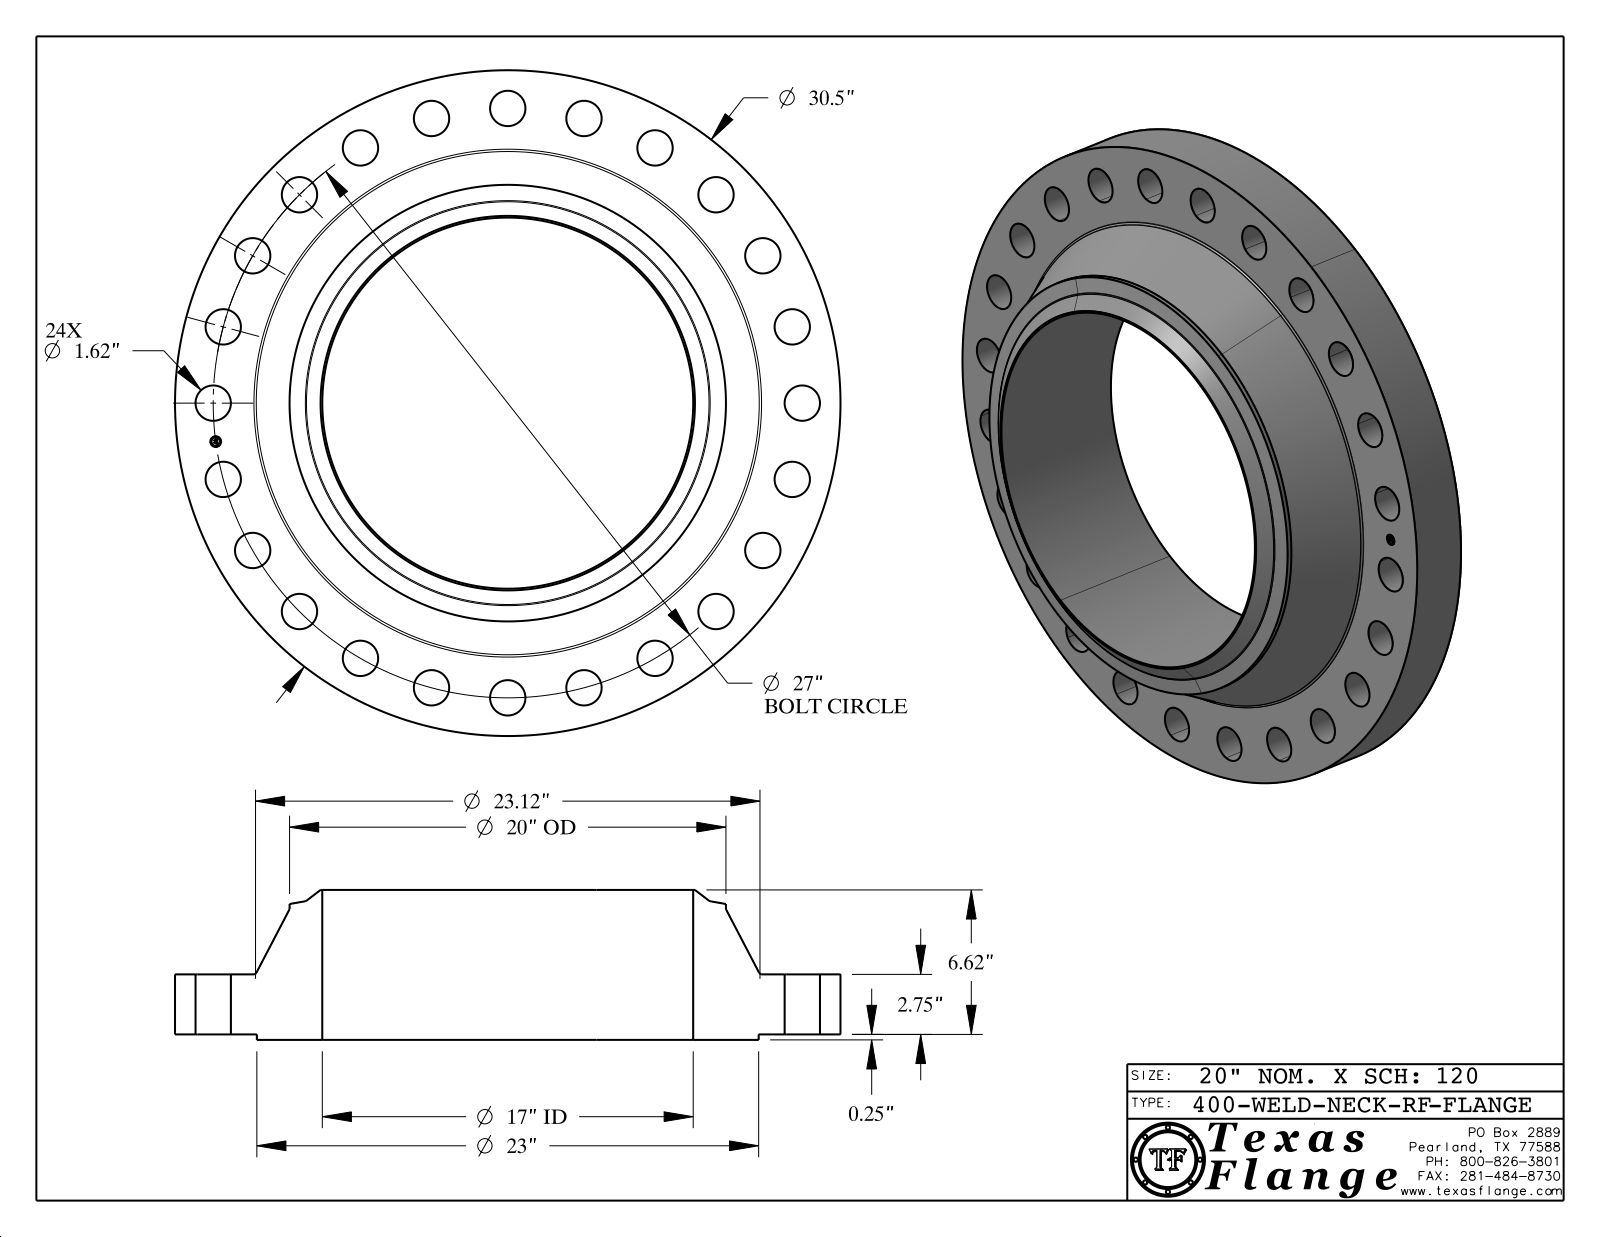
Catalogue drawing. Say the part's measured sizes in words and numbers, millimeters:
The part is named "400-WELD-NECK-RF". Its 3-D file was written by "CATIA V5 STEP AP214 (AUTOMOTIVE_DESIGN)". It is 1 solid with 455 faces: 369 planar, 76 cylindrical and 10 other. Overall it measures 774.7 by 774.7 by 174.5 millimeters. Its volume is 28 690 000 cubic millimeters and its surface area 1 316 000 square millimeters. Round holes: 24 of diameter 41.1, 1 of diameter 12.6, 1 of diameter 431.8. Round bosses or shafts: 8 of diameter 0.8, 1 of diameter 774.7, 1 of diameter 584.2, 1 of diameter 508, 1 of diameter 9.9. The main face-to-face distances are 69.9, 6.4, 76.2, 174.5, 168.1, 98.3, 75.8, 69.5, 0.4, 98.7. The hole center spacings are 342.9, 89.5, 177.5, 262.5, 417.5, 633.6, 679.9, 544.1.
